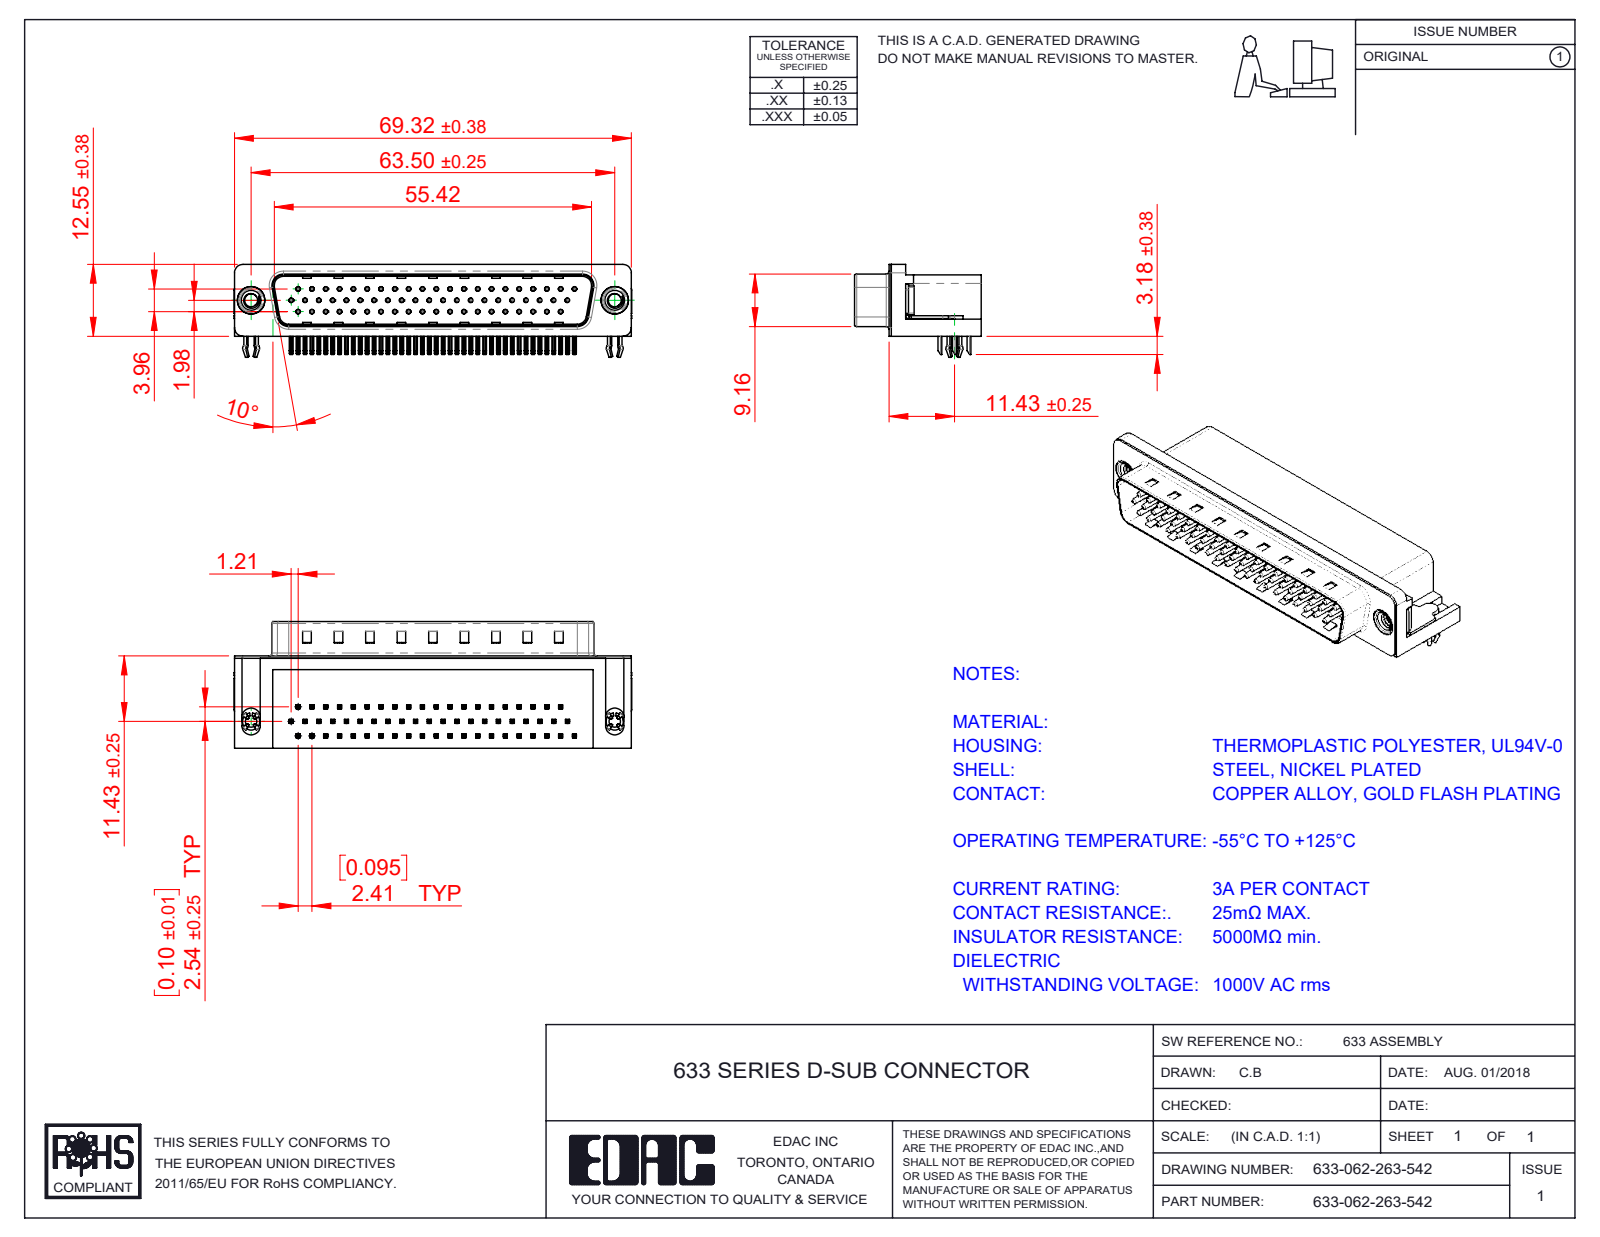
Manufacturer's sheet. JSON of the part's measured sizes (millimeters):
{"part_name": "633-062-263-542; 633 4-40 Threaded Rivet; 633 Shell_62 Contact; 633 Housing_62 Contact (+4 more)", "step_written_by": "SolidWorks 2016 (CONFIG_CONTROL_DESIGN)", "units": "millimeters", "bodies": {"solids": 68, "faces": 5196, "planar": 3255, "cylindrical": 1448, "other": 493}, "overall_size": [69.4, 22.1, 16.25], "volume_mm3": 11065, "surface_area_mm2": 13479, "round_holes": [[0.35, 62], [0.8, 62], [2, 2], [2.26, 2], [4, 2], [4.8, 2], [5, 2]], "round_bosses_or_shafts": [[0.75, 62], [4.9, 2], [4.75, 2], [3.9, 2], [3, 2]], "partial_cylinders_radius": [[0.25, 260], [0.12, 124], [1, 16], [0.5, 9], [1.6, 8], [1.5, 7], [0.9, 4], [2, 4]], "face_to_face_distances": [0.4, 10.35, 15.7, 8.76, 2.9, 2.5, 2.54, 8.36, 2.1, 16.1], "hole_center_spacings": [2.41, 4.82, 7.24, 9.65, 14.48, 16.89, 4.83, 7.23]}
